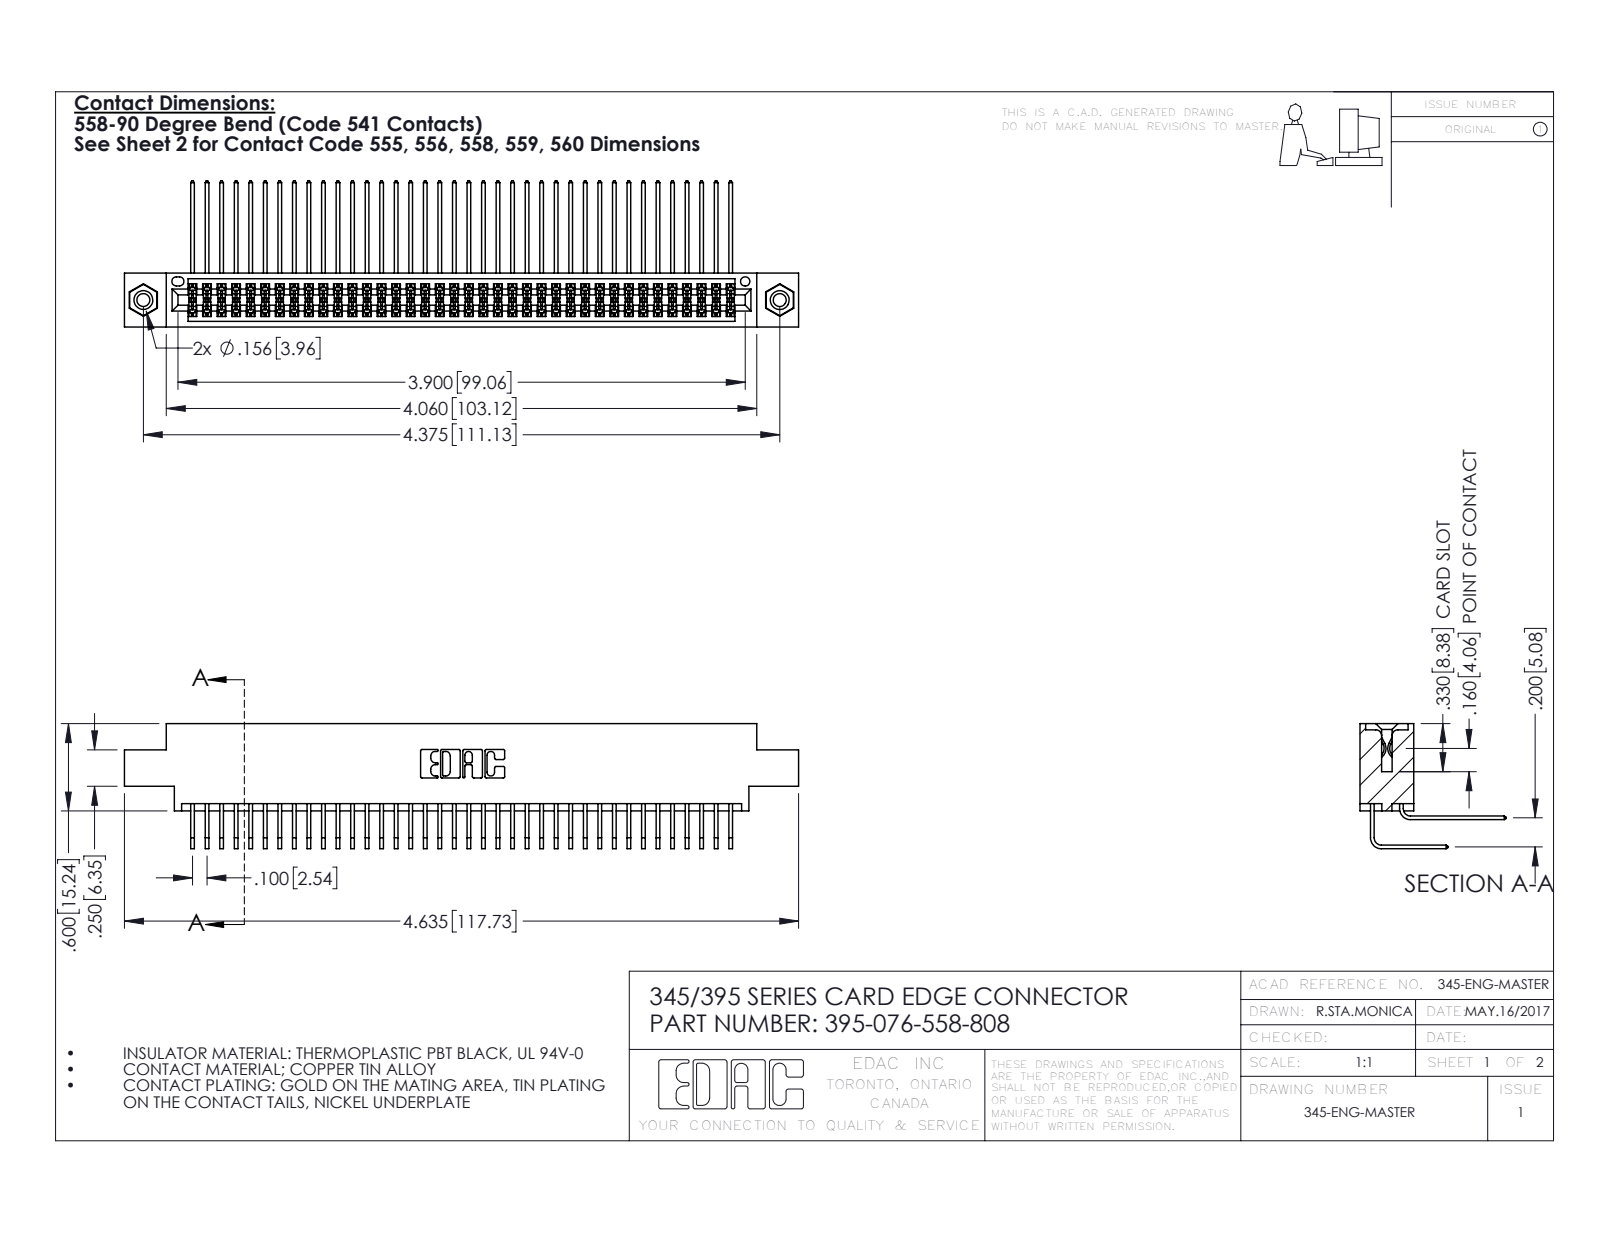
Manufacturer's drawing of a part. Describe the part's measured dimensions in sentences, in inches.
The part is named "395-076-558-808; 345 Part_0.170 Offset - 0.156 Dia-TI; 345-292-001_558 Tail - 2; 345-292-001_558 559 Tail - 1 (+1 more)". Its 3-D file was written by "SolidWorks 2016 (CONFIG_CONTROL_DESIGN)". It is 79 solids with 4142 faces: 2776 planar, 1350 cylindrical and 16 other. Overall it measures 4.635 by 1.005 by 0.859 inches. Its volume is 0.715 cubic inches and its surface area 30.17 square inches. Round holes: 2 of diameter 0.089, 2 of diameter 0.125, 2 of diameter 0.156, 1 of diameter 0.064. Round bosses or shafts: 2 of diameter 0.155. Partial cylindrical surfaces (rounded edges, fillets, slot ends): 114 of radius 0.006, 22 of radius 0.01, 6 of radius 0.007, 6 of radius 0.031, 3 of radius 0.026, 2 of radius 0.014, 2 of radius 0.019, 2 of radius 0.022. The main face-to-face distances are 0.072, 0.298, 0.2, 0.37, 0.098, 0.272, 0.025, 0.225, 0.175, 0.025. The hole center spacings are 0.27, 4.139, 4.375.
